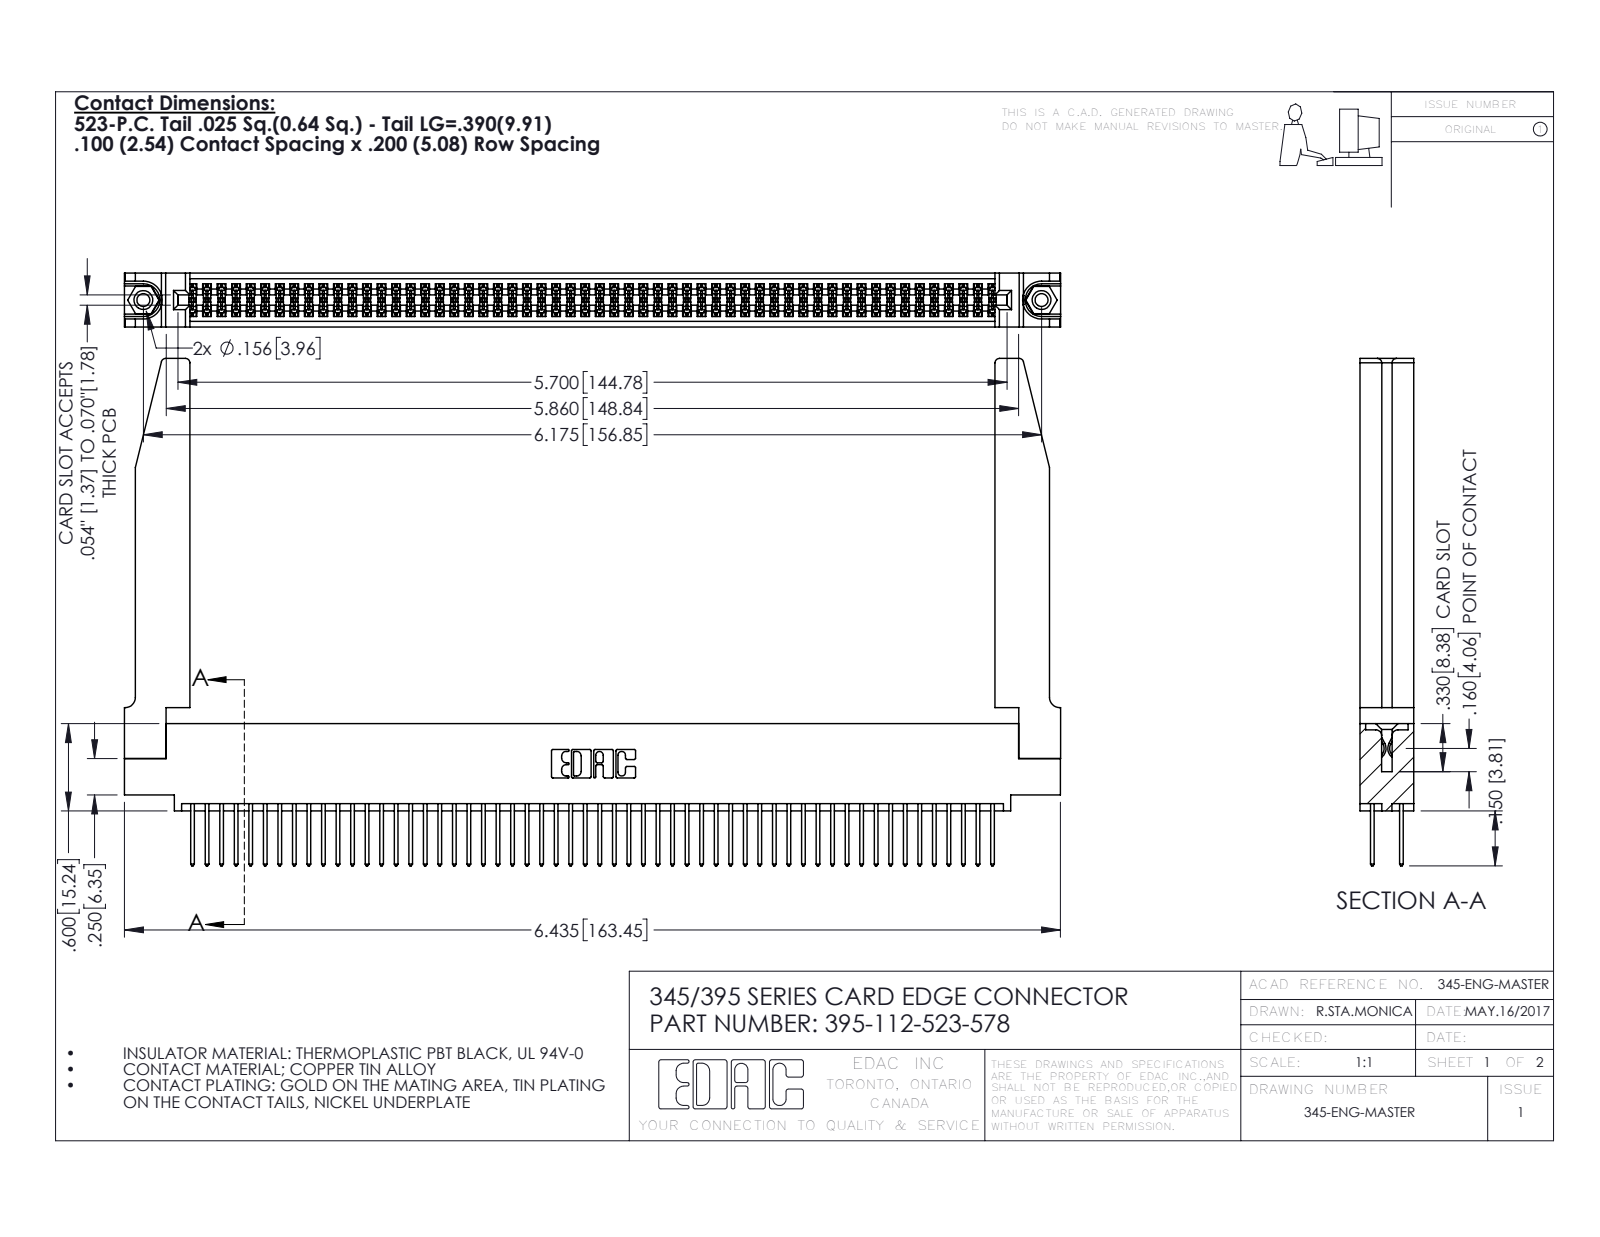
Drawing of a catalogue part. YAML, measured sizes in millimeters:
part_name: "345-220-078_345-220-078; 345-292-001_345-293-123; 345-250-001_345-250-001-102; 395-112-523-578 (+1 more)"
step_written_by: "SolidWorks 2016 (CONFIG_CONTROL_DESIGN)"
units: millimeters
bodies: {solids: 117, faces: 5964, planar: 3922, cylindrical: 1990, other: 52}
overall_size: [163.5, 88.6, 9.4]
volume: 23940
surface_area: 32130
round_holes:
  - {diameter: 2.3, count: 2}
  - {diameter: 3.2, count: 2}
  - {diameter: 4, count: 2}
  - {diameter: 1.6, count: 1}
round_bosses_or_shafts:
  - {diameter: 3.9, count: 2}
partial_cylinders:
  - {radius: 0.2, count: 168}
  - {radius: 0.3, count: 112}
  - {radius: 0.3, count: 22}
  - {radius: 0.8, count: 8}
  - {radius: 0.2, count: 6}
  - {radius: 0.8, count: 6}
  - {radius: 0.7, count: 3}
  - {radius: 0.4, count: 2}
face_to_face_distances: [1.8, 7.6, 9.4, 5.1, 2.5, 6.9, 0.6, 5.7, 4.4, 3.8]
hole_center_spacings: [6.9, 150.9, 156.8]
